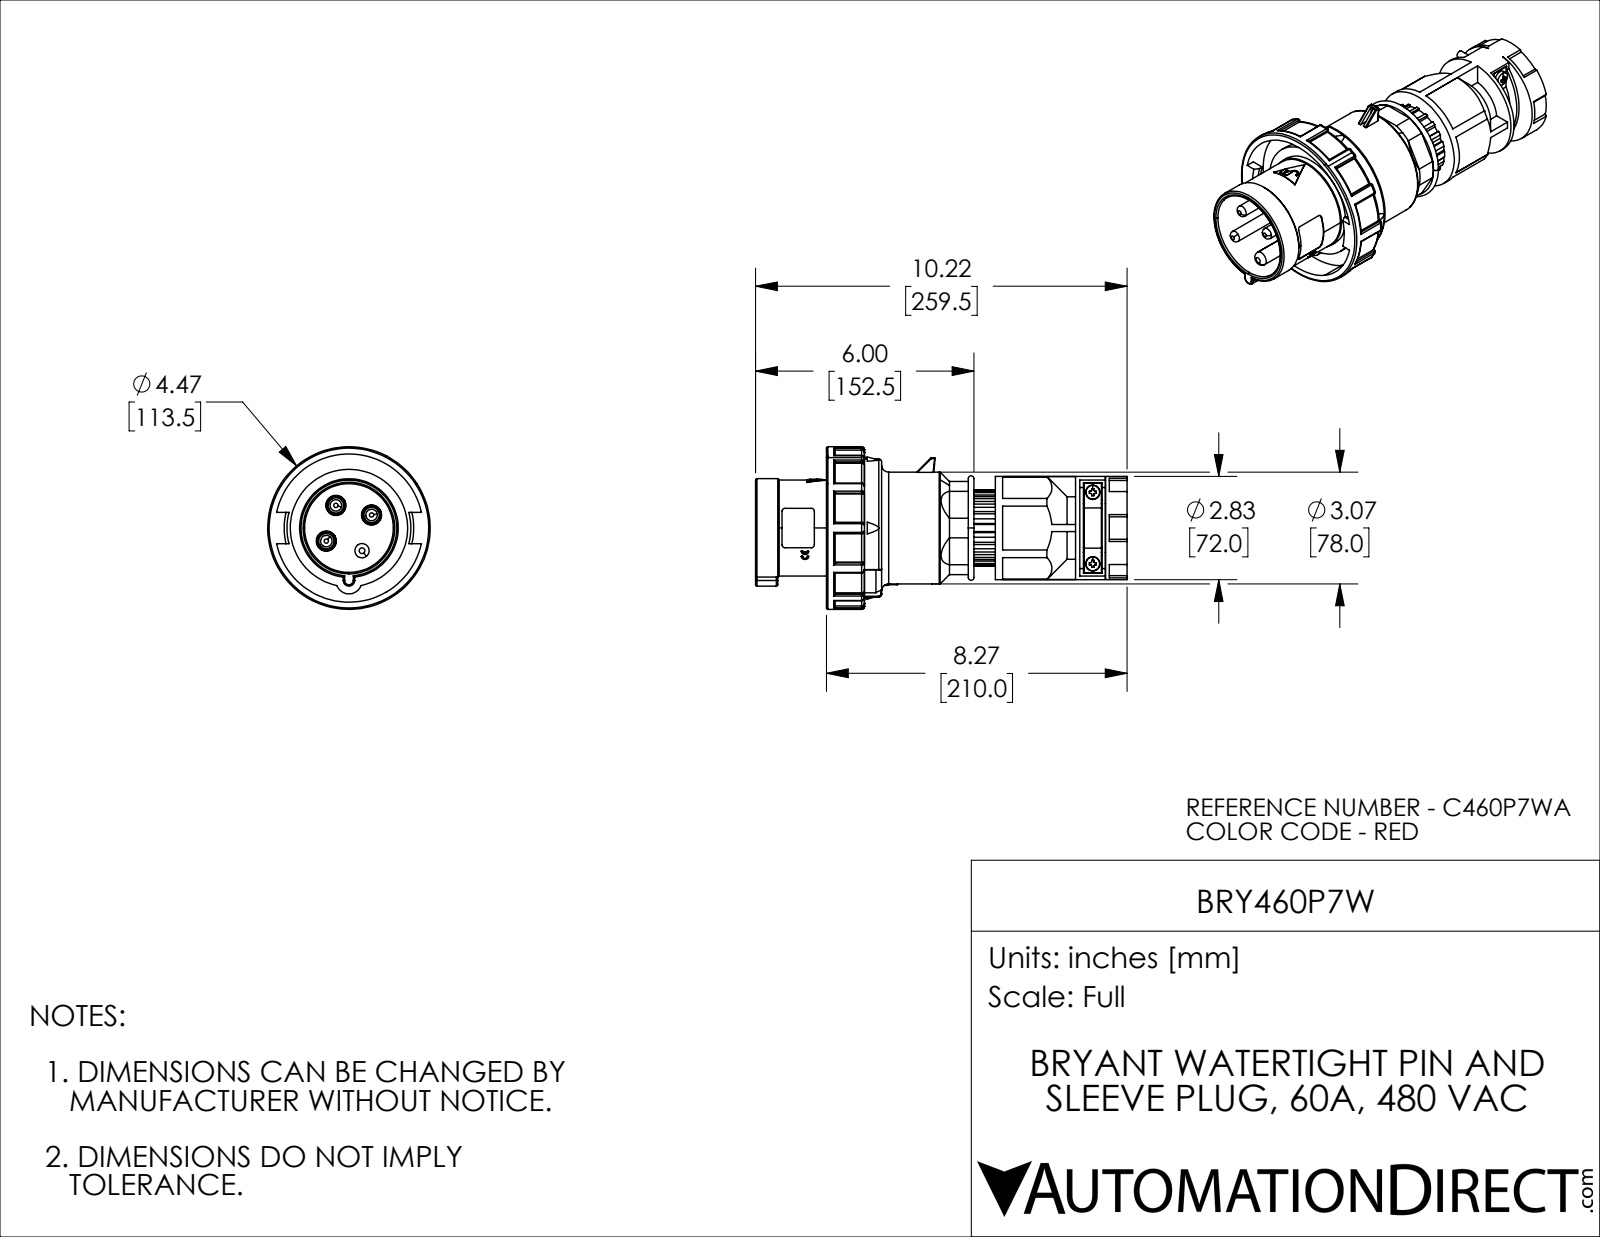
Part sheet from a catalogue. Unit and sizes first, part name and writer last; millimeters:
Units: millimetres
Overall size (bounding box): 259.5 × 113.5 × 113.5
Round holes (diameter × count): ⌀2 ×2, ⌀37 ×1, ⌀62 ×1, ⌀65.5 ×1, ⌀103.5 ×1
Round bosses / shafts (diameter × count): ⌀8 ×3, ⌀5 ×2, ⌀113.5 ×1, ⌀105.75 ×1, ⌀82 ×1, ⌀78 ×1, ⌀72 ×1, ⌀68.9 ×1
Partial cylindrical surfaces — rounded edges, fillets, slot ends (radius × count): R1 ×34, R0.5 ×23, R2 ×18, R34.5 ×6, R0.4 ×4, R3 ×3, R4 ×3, R1.2 ×2
Main face-to-face distances: 65, 15, 92, 3, 97, 18, 86, 26, 5, 15.5
Volume: 753 266 mm³ · Surface area: 144 833 mm²
Bodies: 1 solid, 1173 faces (493 planar, 384 cylindrical, 296 other)
Part name (STEP PRODUCT): BRY460P7W
STEP written by: SolidWorks 2021 (CONFIG_CONTROL_DESIGN)
